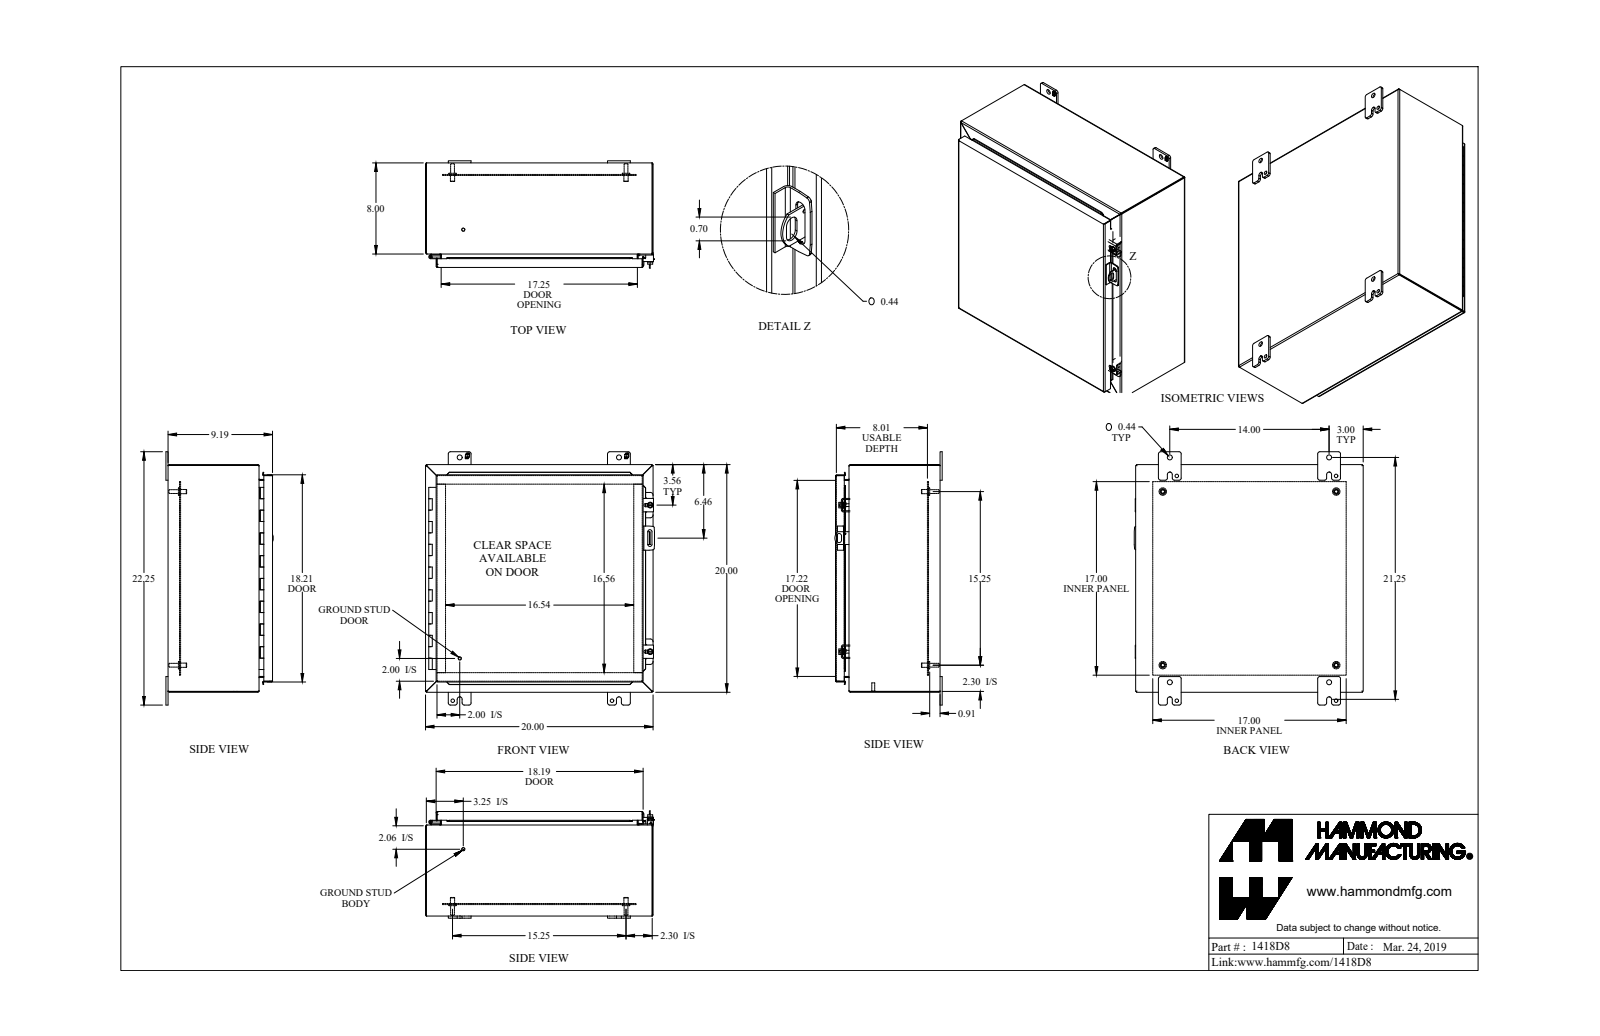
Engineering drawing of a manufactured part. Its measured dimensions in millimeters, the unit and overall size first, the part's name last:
Units: millimetres
Overall size (bounding box): 565.2 × 511.2 × 239.7
Round holes (diameter × count): ⌀8 ×4, ⌀11.1 ×4, ⌀12.7 ×4, ⌀5.4 ×2, ⌀6.7 ×2, ⌀7.8 ×2, ⌀9.5 ×2, ⌀11.3 ×2, ⌀3.2 ×1, ⌀4.7 ×1
Round bosses / shafts (diameter × count): ⌀16.5 ×4, ⌀9.5 ×4, ⌀8.4 ×4, ⌀25.4 ×2, ⌀12.7 ×2, ⌀9.9 ×2, ⌀7.1 ×2, ⌀6.4 ×2
Partial cylindrical surfaces — rounded edges, fillets, slot ends (radius × count): R4.8 ×26, R0.9 ×20, R2.7 ×20, R1.2 ×13, R3.6 ×13, R0.2 ×8, R1.1 ×8, R2 ×8
Main face-to-face distances: 1.8, 231.5, 506.2, 229.6, 233.3, 23.8, 25.6, 504.3, 508, 2.4
Hole centre spacings: 387.4, 355.6, 547.8, 44.1, 77.9, 387.4, 425.8, 501.7
Volume: 2 638 000 mm³ · Surface area: 2 701 000 mm²
Bodies: 38 solids, 970 faces (667 planar, 251 cylindrical, 52 other)
Part name (STEP PRODUCT): 1418D8
STEP written by: SolidWorks 2019 (AUTOMOTIVE_DESIGN)
